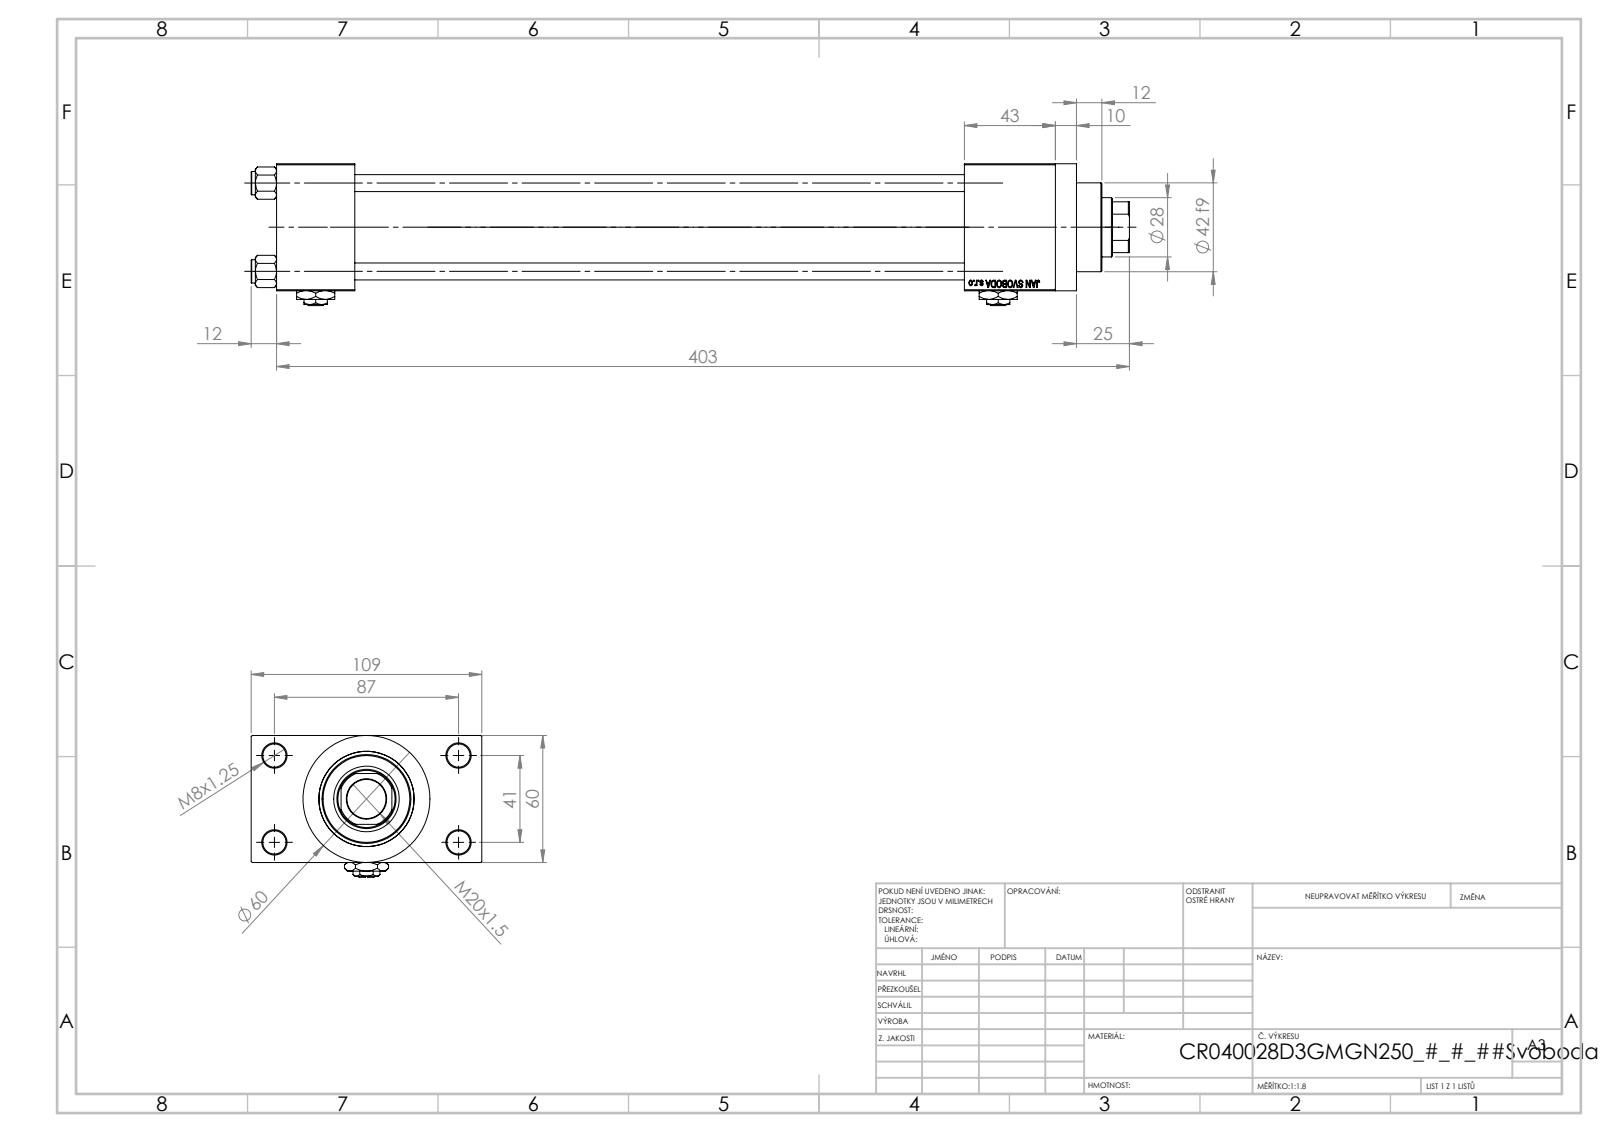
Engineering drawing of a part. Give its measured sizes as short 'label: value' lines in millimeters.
name: V215CR_D_TYCINKA; NUT_M5_D; Zatka_pro_OIL_PORT; V215_VC_A (+2 more)
written by: SolidWorks 2019 (CONFIG_CONTROL_DESIGN)
unit: mm
bodies: 13 solids, 1205 faces (546 planar, 99 cylindrical, 560 other)
size: 415 × 109 × 67
volume: 808 093 mm³; area: 237 158 mm²
holes: 4× ⌀8, 4× ⌀11, 4× ⌀16.66, 4× ⌀24, 3× ⌀7, 1× ⌀18.5, 1× ⌀28, 1× ⌀31, 1× ⌀40, 1× ⌀45
bosses: 4× ⌀11, 1× ⌀60, 1× ⌀46, 1× ⌀42
rounds: 1× R13.5
face distances: 60, 24.5, 288, 84.5, 37, 325, 368, 331, 43, 109
hole spacings: 22.65, 29.49, 41.7, 47.15, 48.09, 64.35, 76.49, 41
